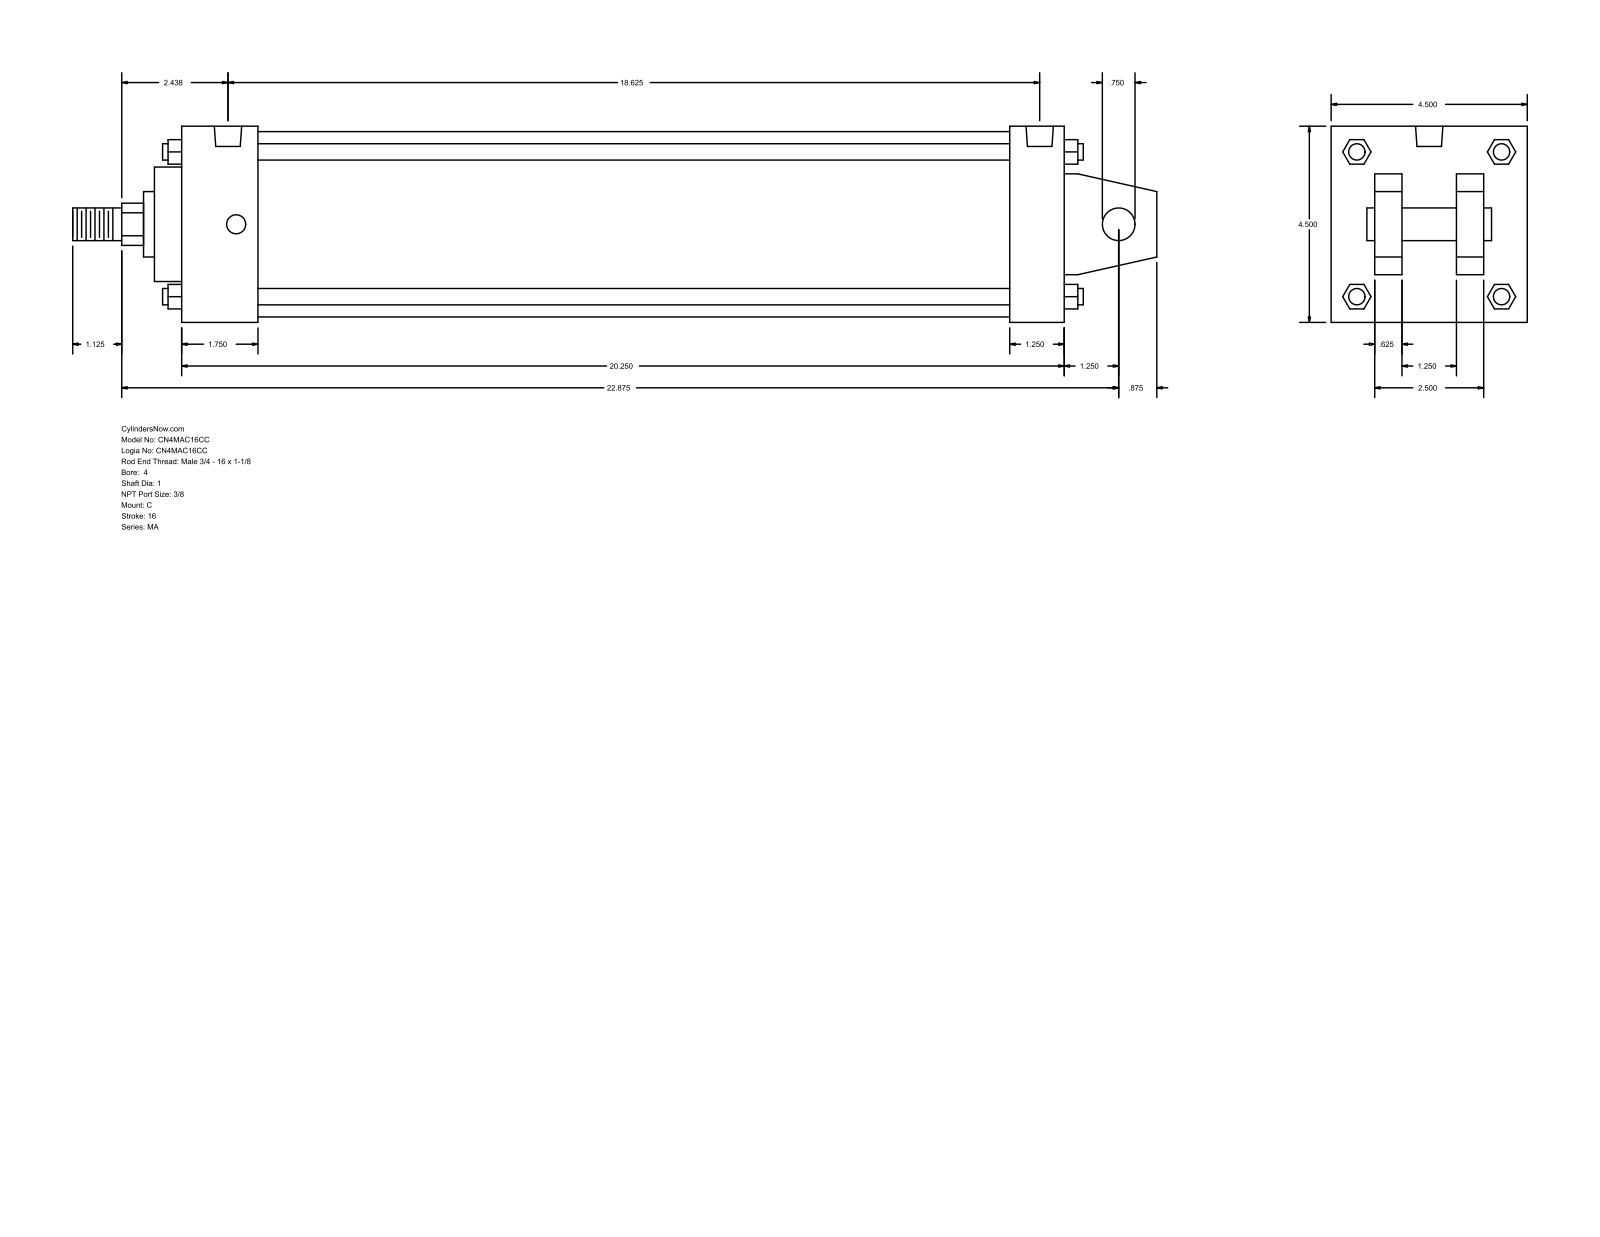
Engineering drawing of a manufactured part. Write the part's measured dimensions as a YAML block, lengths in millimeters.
part_name: "MA_C__0400_1"
step_written_by: "GSSL Pune (CONFIG_CONTROL_DESIGN)"
units: millimeters
bodies: {solids: 0, faces: 141, planar: 109, cylindrical: 32, other: 0}
overall_size: [631.83, 114.3, 114.3]
round_holes:
  - {diameter: 11.11, count: 4}
  - {diameter: 15.93, count: 2}
round_bosses_or_shafts:
  - {diameter: 9.53, count: 4}
  - {diameter: 19.05, count: 2}
  - {diameter: 107.95, count: 1}
  - {diameter: 66.67, count: 1}
  - {diameter: 38.1, count: 1}
  - {diameter: 25.4, count: 1}
partial_cylinders:
  - {radius: 12.29, count: 1}
face_to_face_distances: [114.3, 514.35, 15.87, 73.03, 41.27, 25.4, 88.9, 47.63, 482.6, 31.75]
hole_center_spacings: [4.76, 463.56, 468.32, 473.08]
